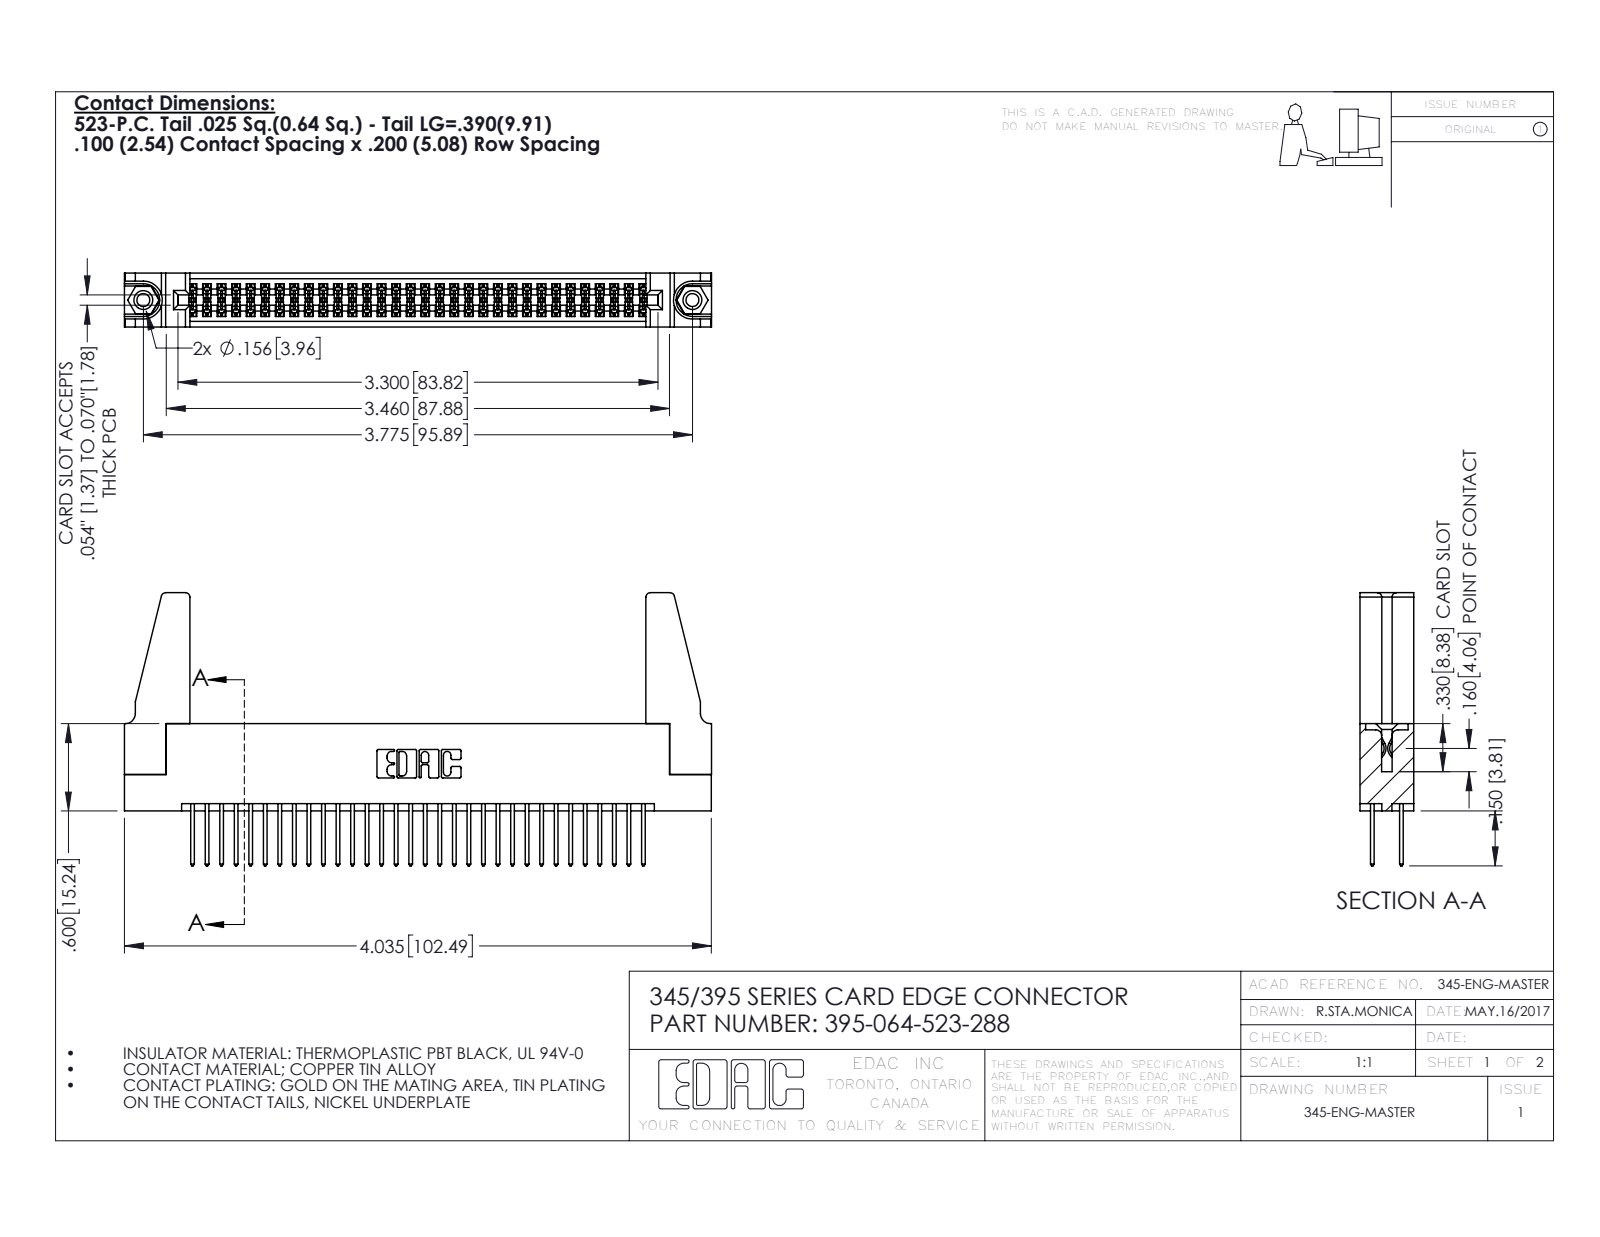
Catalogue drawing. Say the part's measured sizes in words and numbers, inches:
The part is named "395-064-523-288; 345-250-001_345-250-001-102; 345-220-078_345-220-088; 345-292-001_345-293-123 (+1 more)". Its 3-D file was written by "SolidWorks 2016 (CONFIG_CONTROL_DESIGN)". It is 69 solids with 3450 faces: 2264 planar, 1170 cylindrical and 16 other. Overall it measures 4.036 by 1.877 by 0.37 inches. Its volume is 0.809 cubic inches and its surface area 28.36 square inches. Round holes: 2 of diameter 0.089, 2 of diameter 0.125, 2 of diameter 0.156, 1 of diameter 0.064. Round bosses or shafts: 2 of diameter 0.155. Partial cylindrical surfaces (rounded edges, fillets, slot ends): 96 of radius 0.006, 64 of radius 0.01, 22 of radius 0.01, 8 of radius 0.03, 6 of radius 0.007, 6 of radius 0.031, 3 of radius 0.026, 2 of radius 0.014. The main face-to-face distances are 0.072, 0.298, 0.37, 0.2, 0.098, 0.272, 0.025, 0.225, 0.175, 0.149. The hole center spacings are 0.27, 3.54, 3.775.
